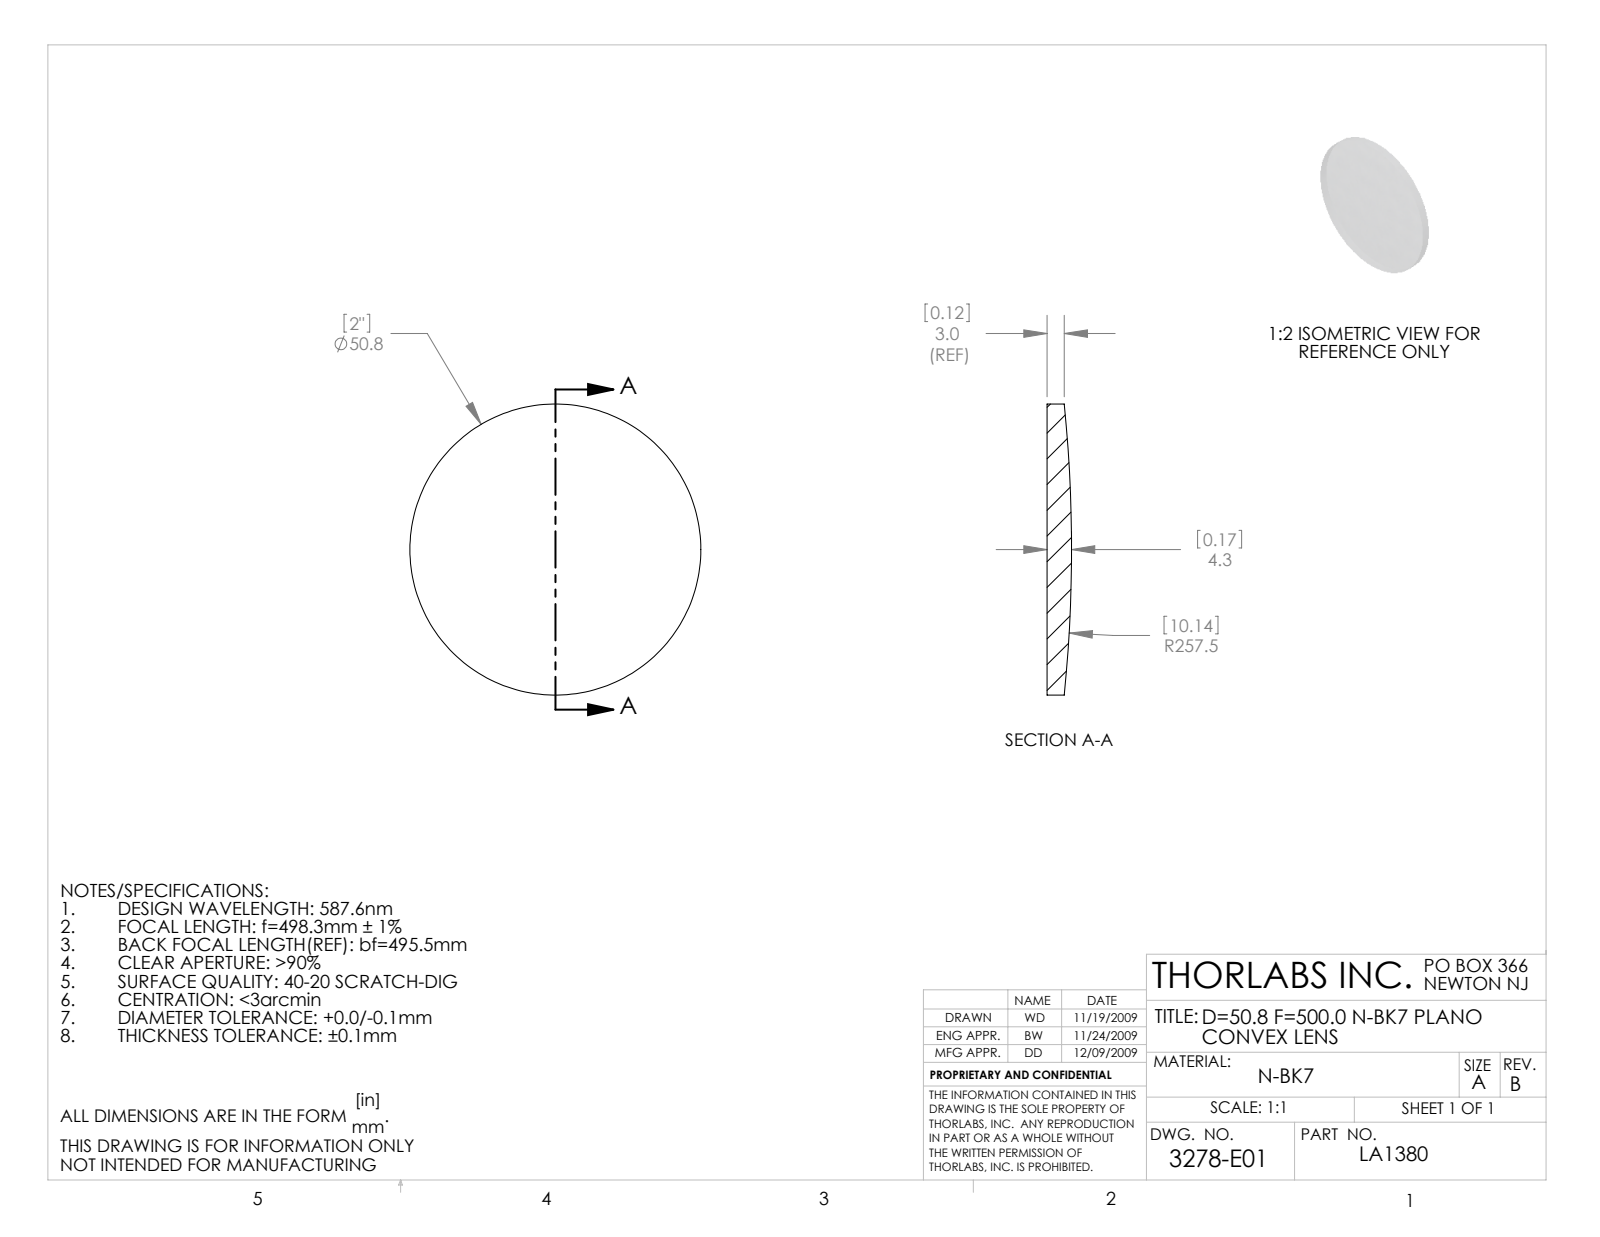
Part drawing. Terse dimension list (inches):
name: 3278-E0W
written by: SolidWorks 2009 (AUTOMOTIVE_DESIGN)
unit: in
bodies: 1 solid, 5 faces (1 planar, 2 cylindrical, 2 other)
size: 2 × 2 × 0.167
volume: 0.448 in³; area: 7.031 in²
bosses: 1× ⌀2
